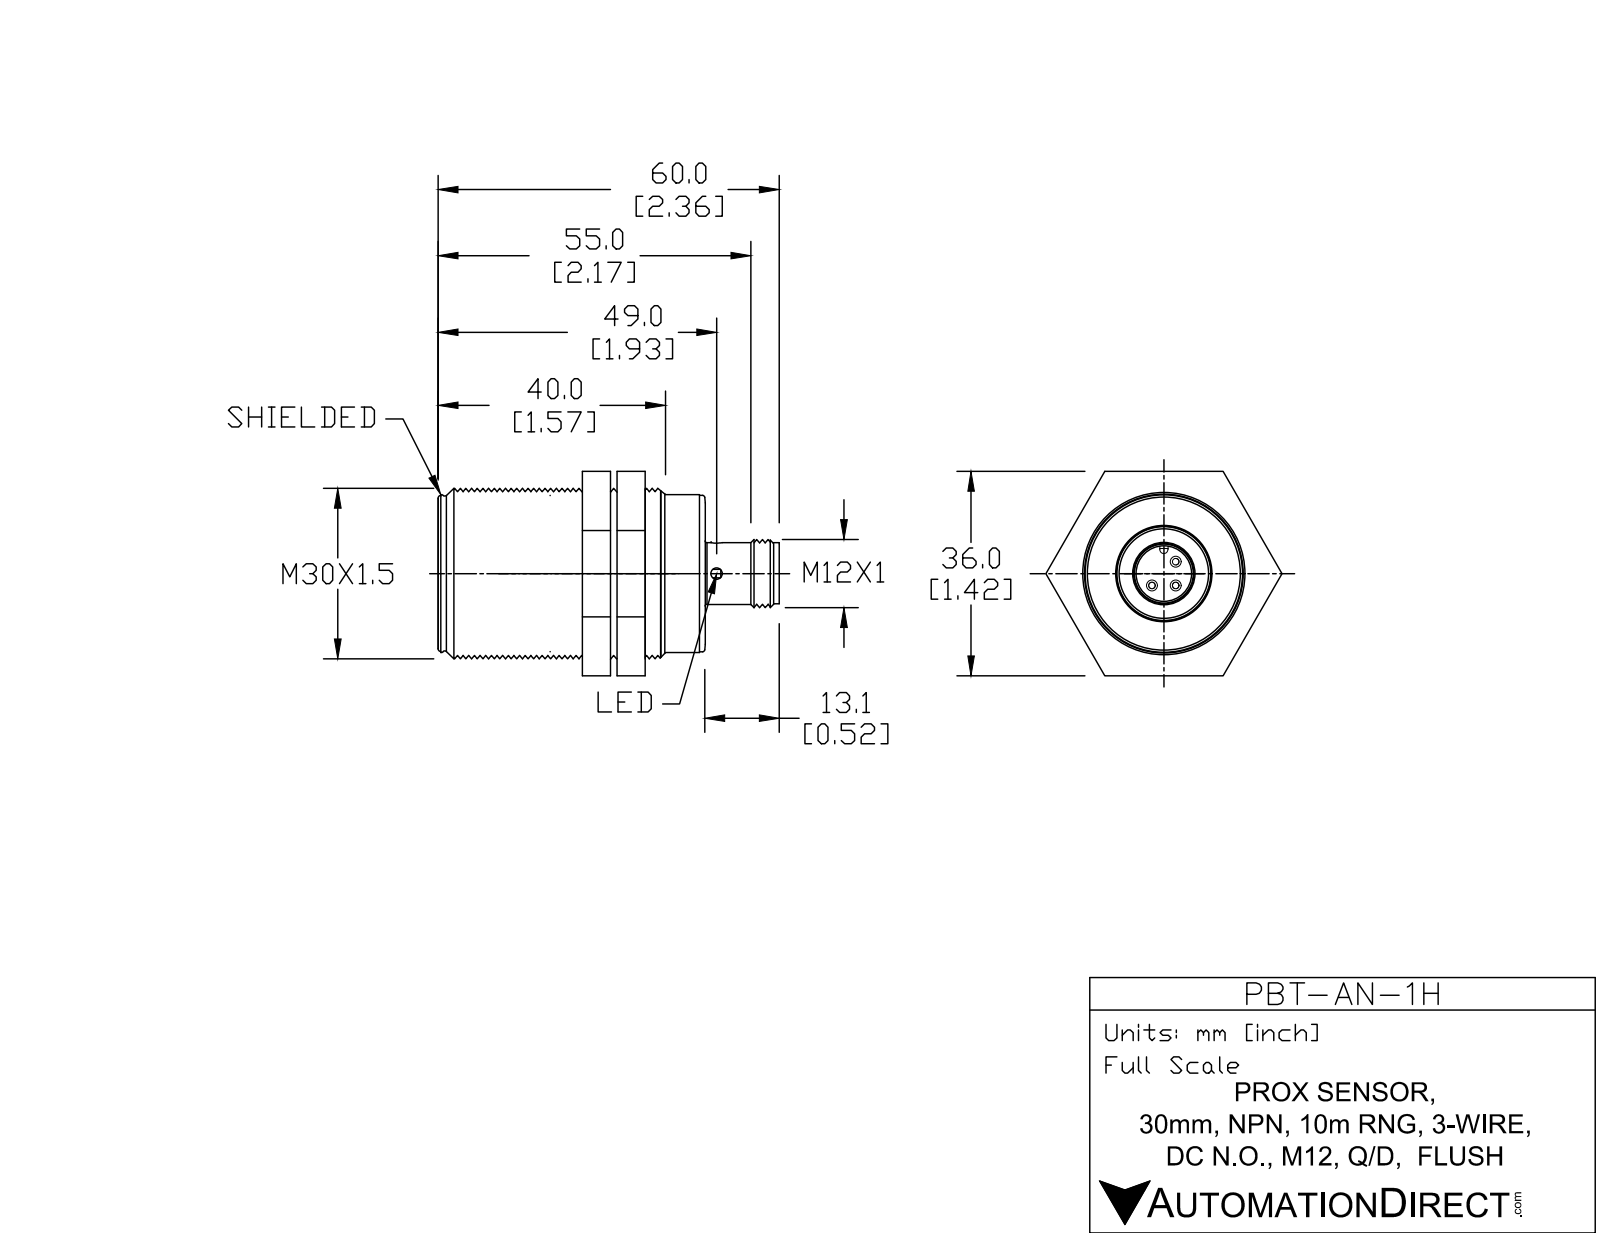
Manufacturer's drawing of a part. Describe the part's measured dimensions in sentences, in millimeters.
The part is named "PBT-AN-1H". Its 3-D file was written by "SolidWorks 2011 (AUTOMOTIVE_DESIGN)". It is 8 solids with 68 faces: 39 planar, 18 cylindrical and 11 other. Overall it measures 59.25 by 41.55 by 36.66 millimeters. Its volume is 37 038 cubic millimeters and its surface area 11 781 square millimeters. Round holes: 1 of diameter 1.25, 1 of diameter 8.5, 1 of diameter 10.5, 1 of diameter 28.5. Round bosses or shafts: 3 of diameter 1, 1 of diameter 30, 1 of diameter 28, 1 of diameter 27.5, 1 of diameter 27.46, 1 of diameter 12, 1 of diameter 10.9, 1 of diameter 10.55. Partial cylindrical surfaces (rounded edges, fillets, slot ends): 1 of radius 0.5. The main face-to-face distances are 10, 4.5, 14.5, 0.75, 46, 46.75, 20, 36, 36.75, 26.
